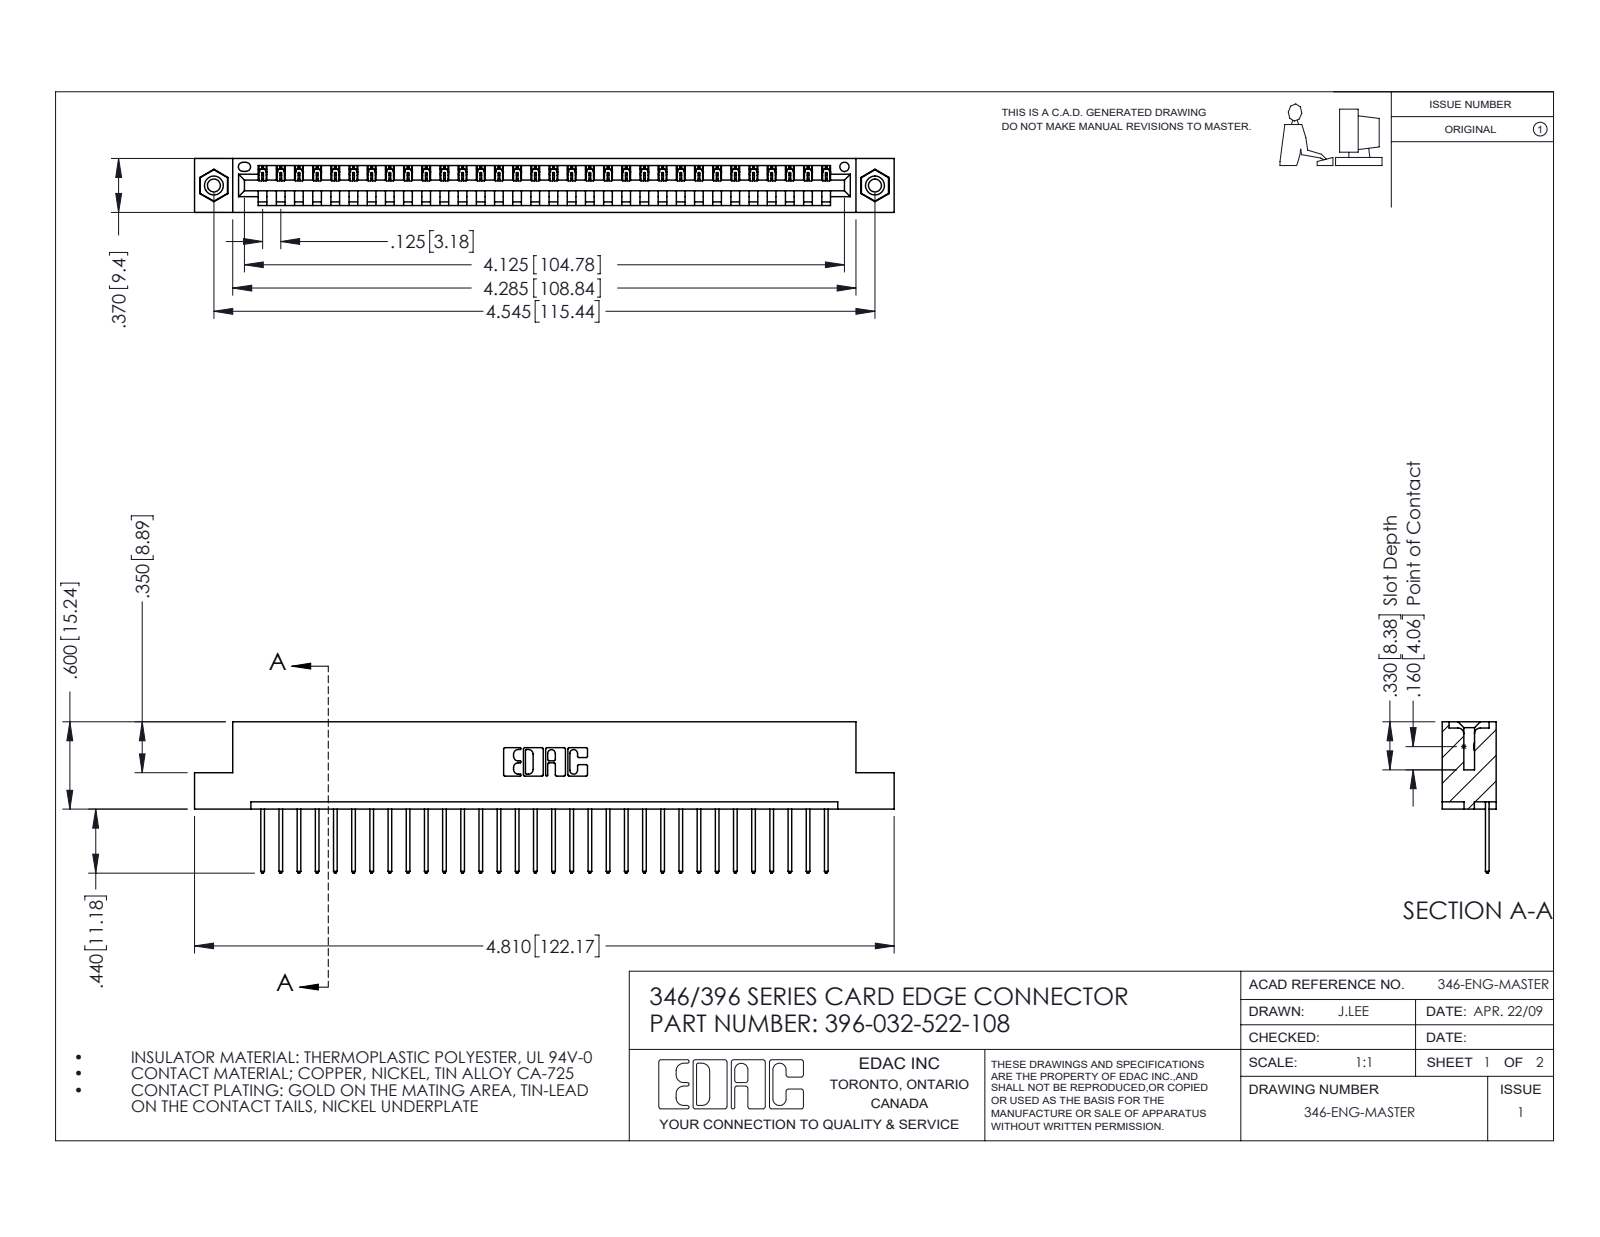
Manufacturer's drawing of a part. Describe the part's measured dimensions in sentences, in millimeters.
The part is named "396-032-522-108; 345-250-001_345-250-003-102; 346 Part_Flush Mounting Lugs - 0.156 Dia-TI; 345-292-001_345-293-122". Its 3-D file was written by "SolidWorks 2016 (CONFIG_CONTROL_DESIGN)". It is 35 solids with 2038 faces: 1388 planar, 634 cylindrical and 16 other. Overall it measures 122.2 by 26.4 by 9.4 millimeters. Its volume is 11 600 cubic millimeters and its surface area 14 560 square millimeters. Round holes: 2 of diameter 2.3, 2 of diameter 3.2, 2 of diameter 4, 1 of diameter 1.6. Round bosses or shafts: 2 of diameter 3.9. Partial cylindrical surfaces (rounded edges, fillets, slot ends): 64 of radius 0.2, 64 of radius 0.3, 22 of radius 0.3, 6 of radius 0.2, 6 of radius 0.8, 3 of radius 0.7, 2 of radius 0.8, 2 of radius 1. The main face-to-face distances are 1.2, 8.2, 9.4, 6.4, 1.8, 7.6, 0.6, 3.8, 5.6, 2.5. The hole center spacings are 6.2, 110.2, 115.4.
